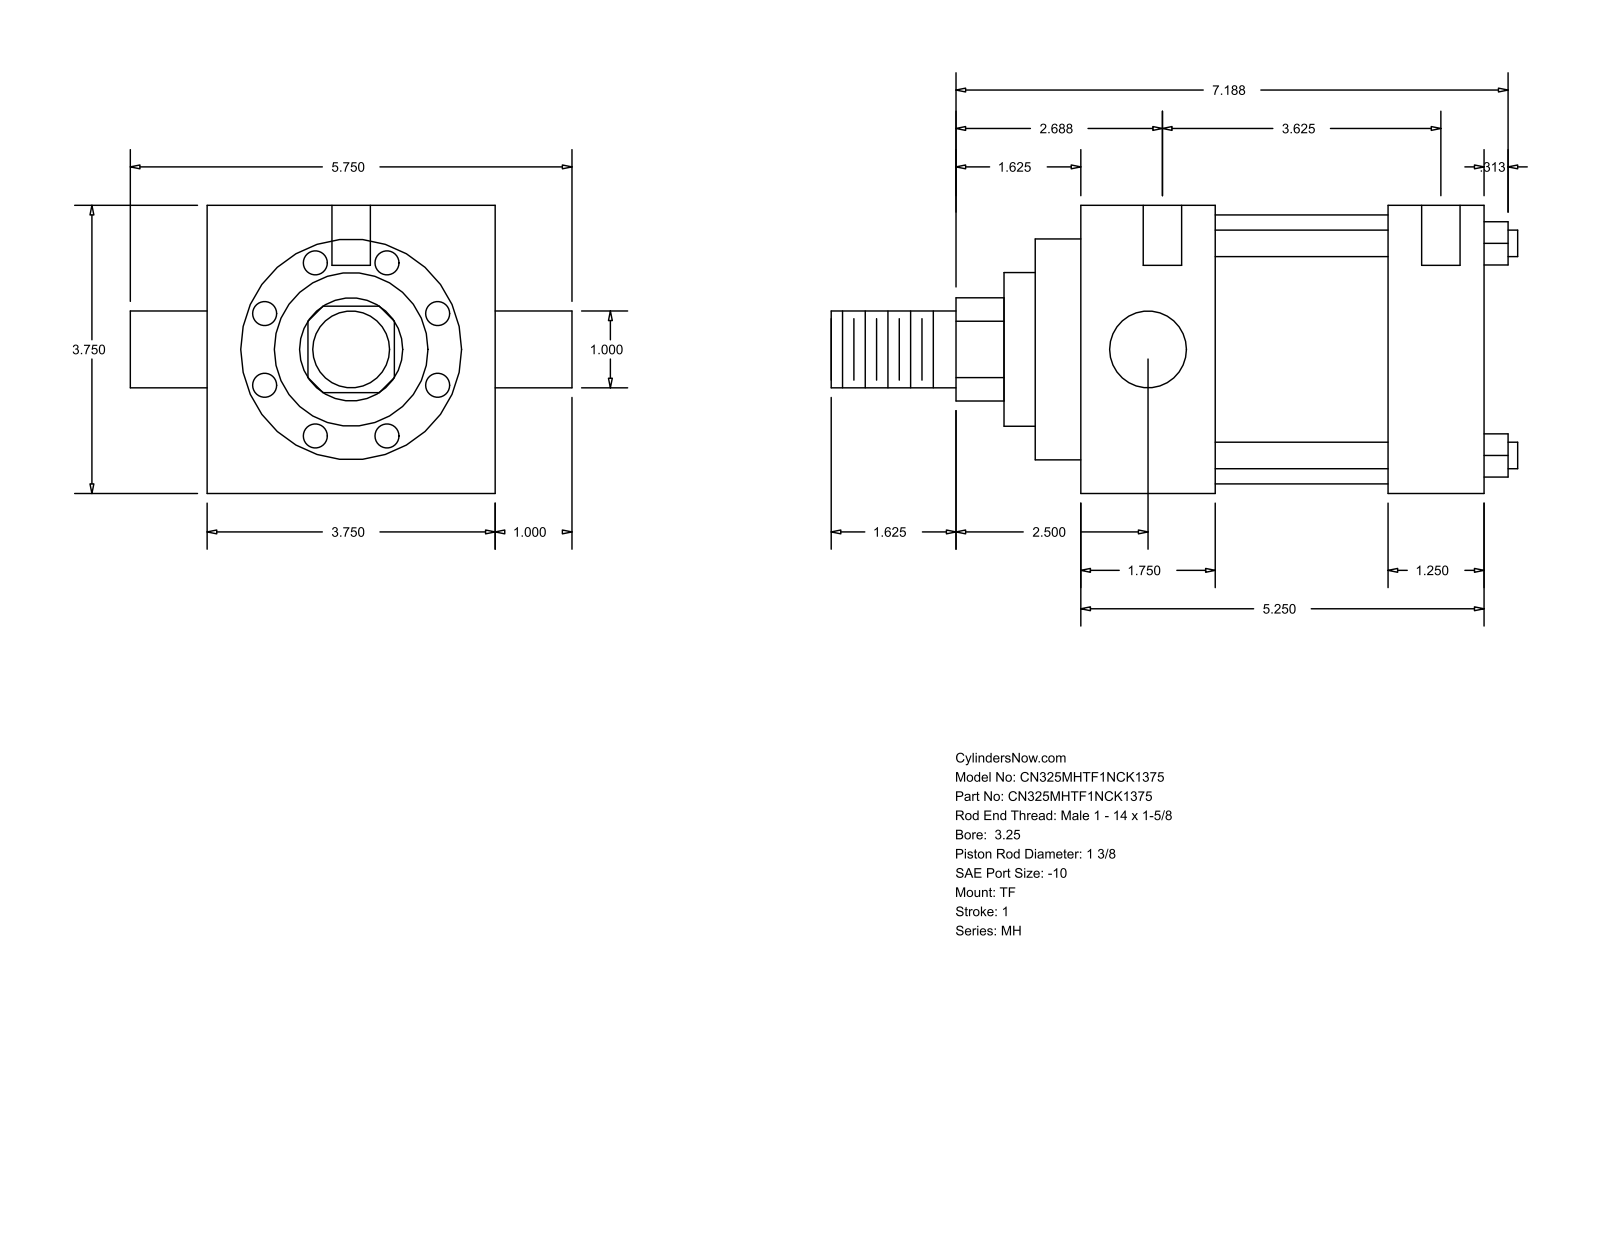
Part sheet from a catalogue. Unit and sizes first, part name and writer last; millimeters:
Units: millimetres
Overall size (bounding box): 227.01 × 146.05 × 95.25
Round holes (diameter × count): ⌀5.56 ×3, ⌀12.7 ×2
Round bosses / shafts (diameter × count): ⌀8.76 ×4, ⌀25.4 ×2, ⌀88.9 ×1, ⌀73.03 ×1, ⌀50.8 ×1, ⌀34.92 ×1
Partial cylindrical surfaces — rounded edges, fillets, slot ends (radius × count): R17.06 ×1
Main face-to-face distances: 95.24, 133.35, 44.45, 101.61, 57.16, 88.9, 31.74, 15.08, 59.53, 116.69
Hole centre spacings: 1.59, 4.76, 92.08, 93.67, 96.84, 98.43
Bodies: 0 solids, 86 faces (61 planar, 25 cylindrical, 0 other)
Part name (STEP PRODUCT): MH_TF__0325_1.375
STEP written by: GSSL Pune (CONFIG_CONTROL_DESIGN)
